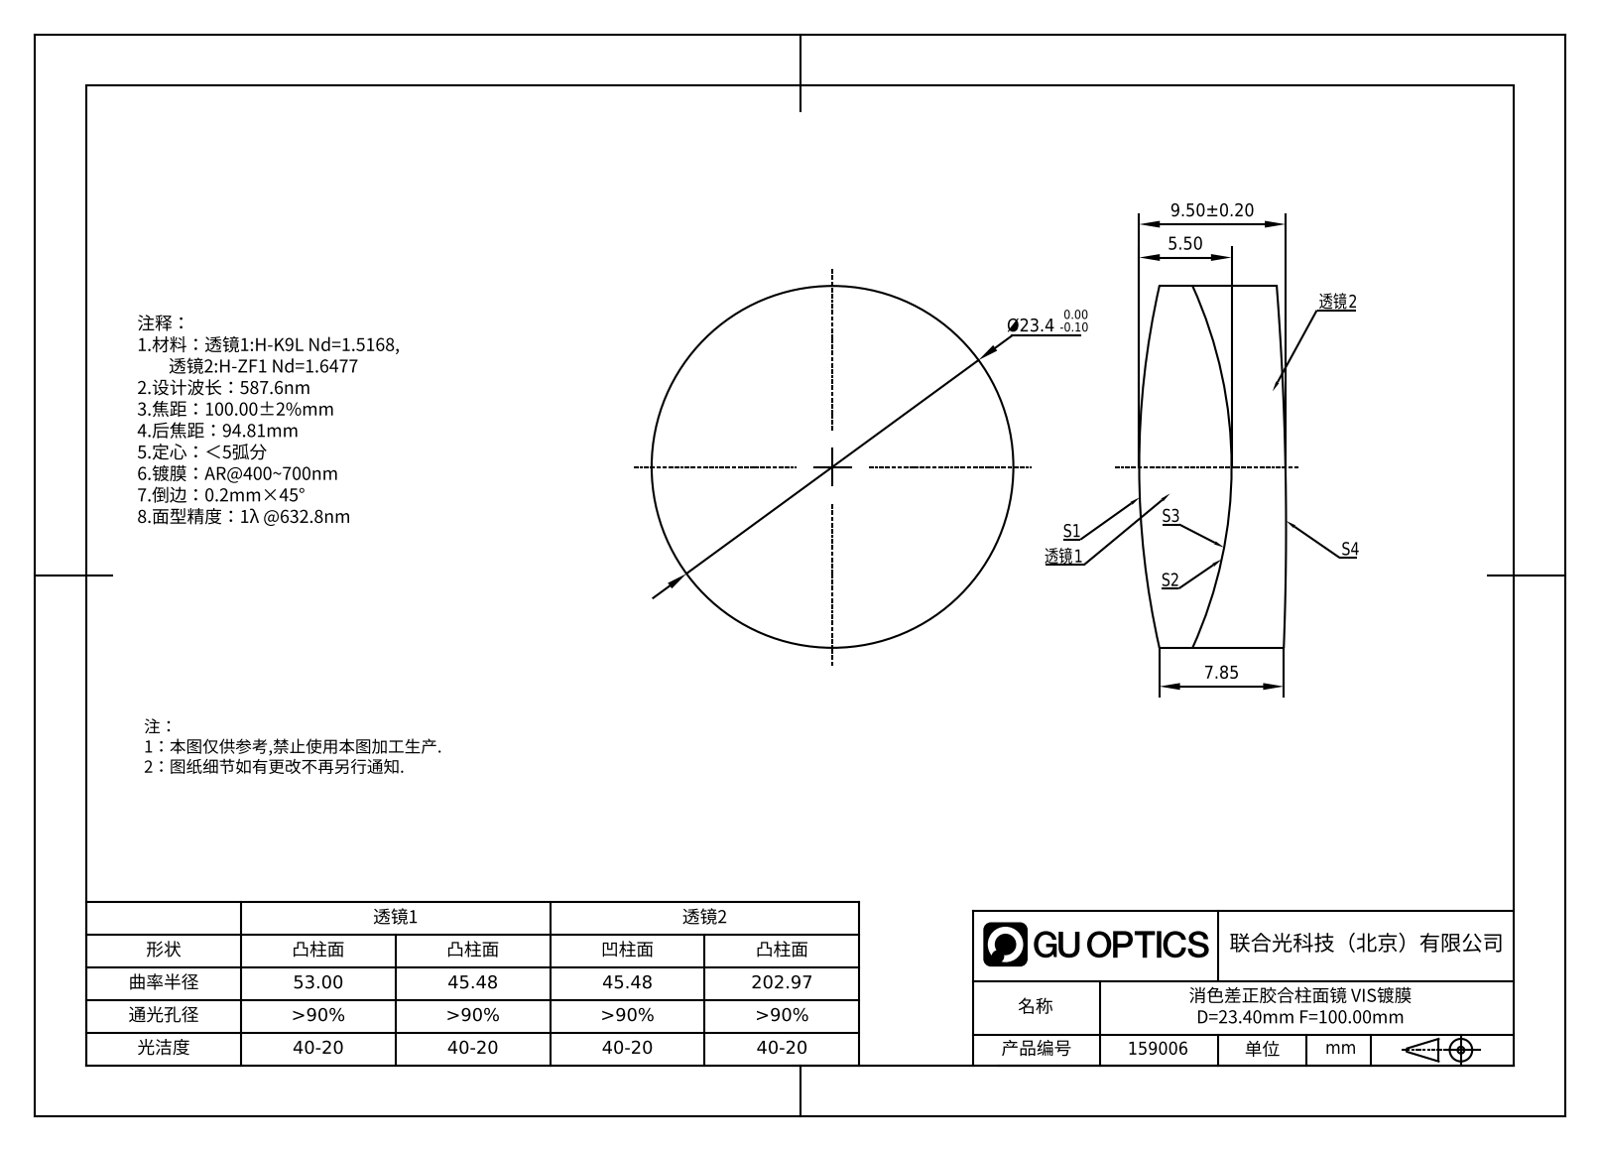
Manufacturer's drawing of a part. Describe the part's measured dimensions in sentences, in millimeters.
The part is named "159006". Its 3-D file was written by "SolidWorks 2020 (CONFIG_CONTROL_DESIGN)". It is 1 solid with 5 faces: 0 planar, 5 cylindrical and 0 other. Overall it measures 23.4 by 23.4 by 9.5 millimeters. Its volume is 3 893 cubic millimeters and its surface area 1 498 square millimeters. Round bosses or shafts: 1 of diameter 23.4. Partial cylindrical surfaces (rounded edges, fillets, slot ends): 1 of radius 53, 1 of radius 202.97.
